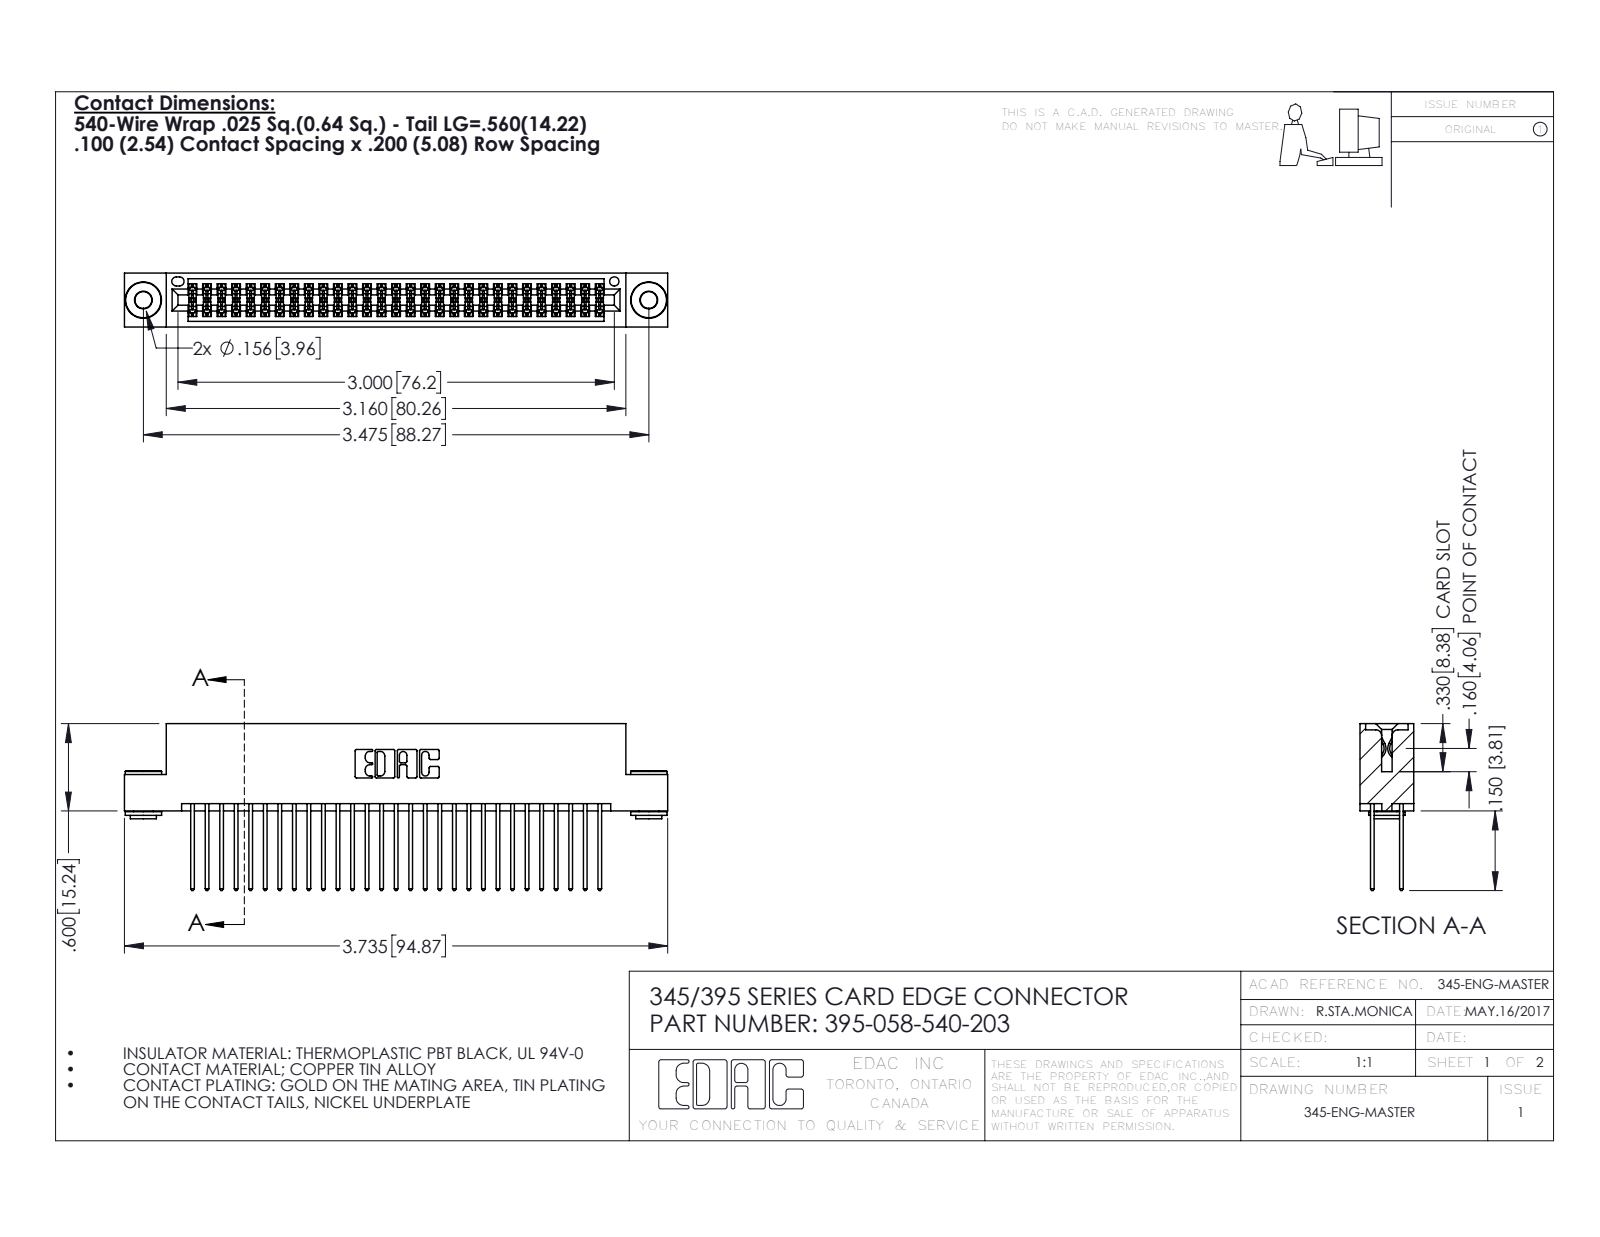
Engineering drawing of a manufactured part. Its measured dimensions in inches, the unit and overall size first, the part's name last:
Units: inches
Overall size (bounding box): 3.735 × 1.147 × 0.37
Round holes (diameter × count): ⌀0.116 ×2, ⌀0.156 ×2, ⌀0.064 ×1
Round bosses / shafts (diameter × count): ⌀0.25 ×2, ⌀0.18 ×2, ⌀0.136 ×2
Partial cylindrical surfaces — rounded edges, fillets, slot ends (radius × count): R0.006 ×87, R0.01 ×58, R0.01 ×22, R0.007 ×6, R0.031 ×6, R0.026 ×3, R0.014 ×2, R0.019 ×2
Main face-to-face distances: 0.072, 0.298, 0.2, 0.025, 0.098, 0.272, 0.37, 0.225, 0.175, 0.149
Hole centre spacings: 0.27, 3.24, 3.475
Volume: 0.57 in³ · Surface area: 22.89 in²
Bodies: 61 solids, 3064 faces (2004 planar, 1052 cylindrical, 8 other)
Part name (STEP PRODUCT): 345 Part_Flush Mounting Lugs - 0.156 Dia-TH; 345-250-002_345-250-002-102; 345-292-001_345-293-140; 395-058-540-203
STEP written by: SolidWorks 2016 (CONFIG_CONTROL_DESIGN)
